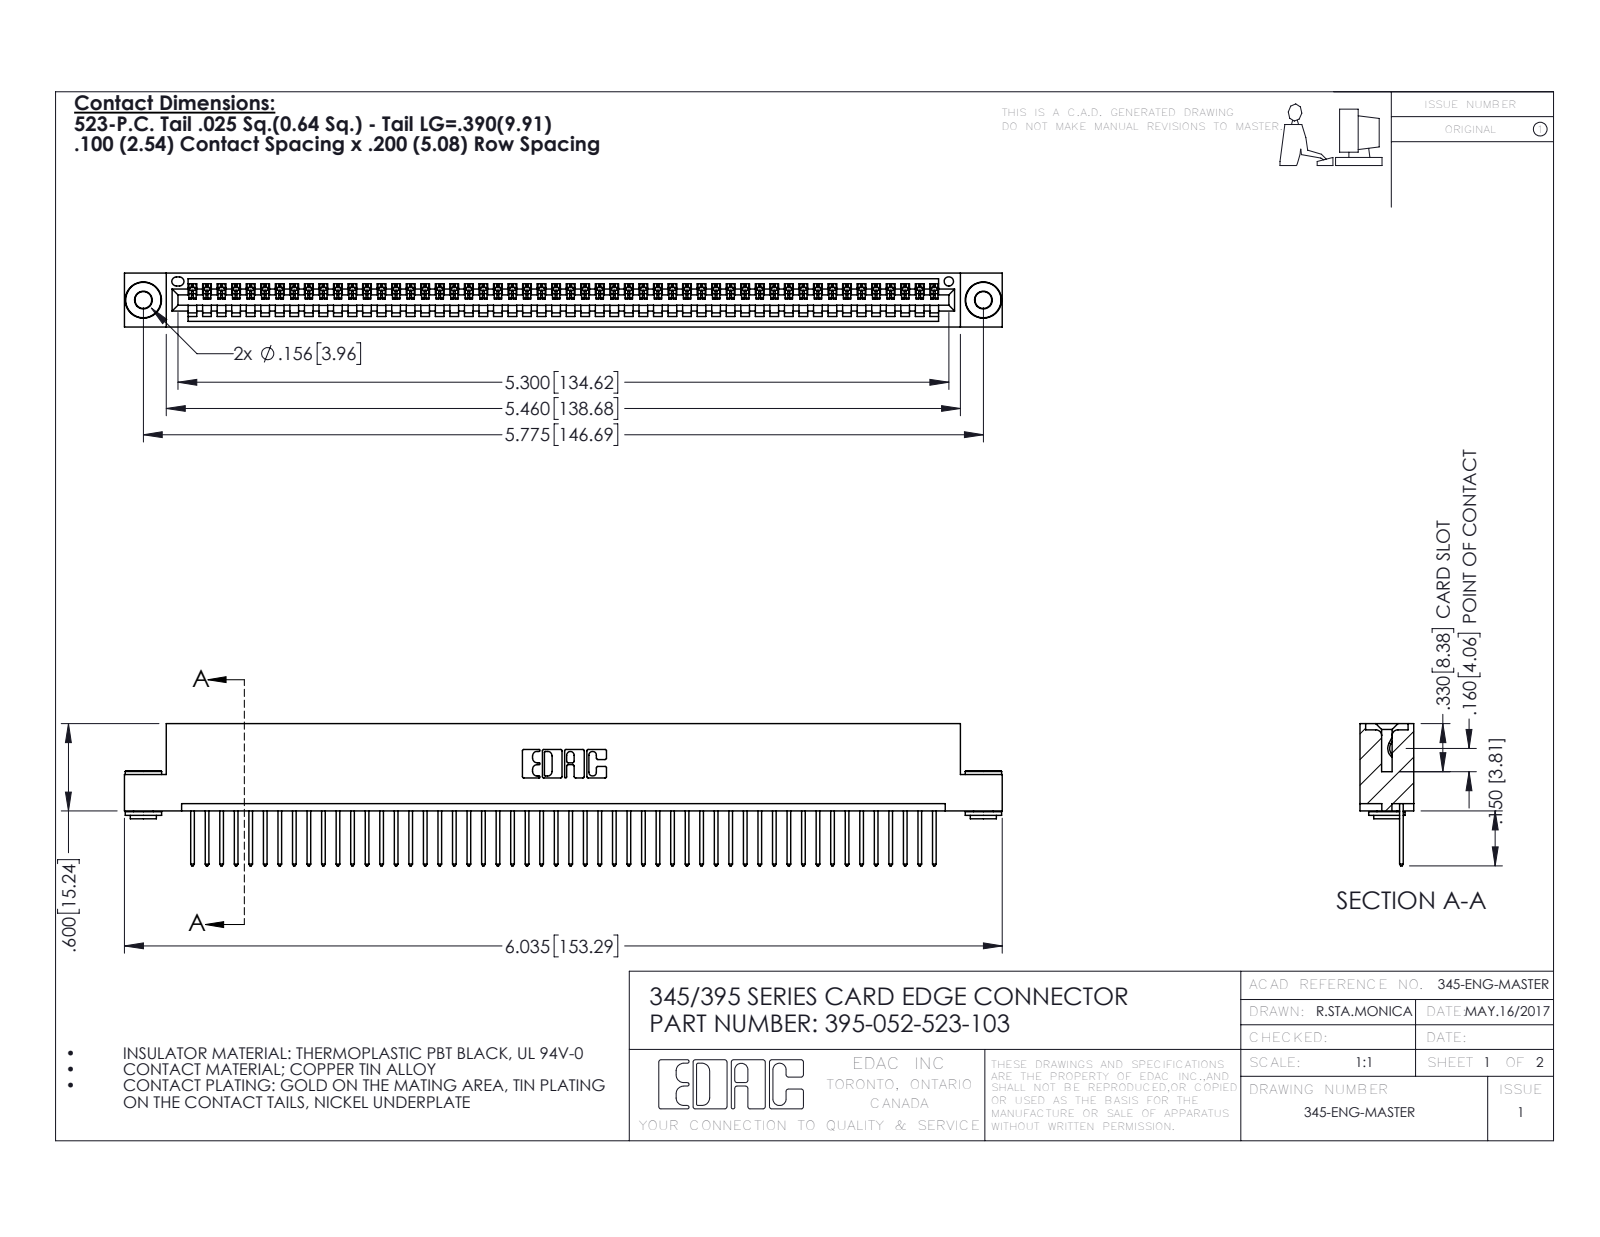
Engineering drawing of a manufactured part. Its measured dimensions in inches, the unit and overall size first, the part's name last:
Units: inches
Overall size (bounding box): 6.035 × 0.977 × 0.37
Round holes (diameter × count): ⌀0.116 ×2, ⌀0.156 ×2, ⌀0.064 ×1
Round bosses / shafts (diameter × count): ⌀0.25 ×2, ⌀0.18 ×2, ⌀0.136 ×2
Partial cylindrical surfaces — rounded edges, fillets, slot ends (radius × count): R0.006 ×104, R0.01 ×104, R0.01 ×22, R0.007 ×6, R0.031 ×6, R0.026 ×3, R0.031 ×2, R0.04 ×2
Main face-to-face distances: 0.072, 0.298, 0.37, 0.2, 0.025, 0.098, 0.272, 0.225, 0.149, 0.072
Hole centre spacings: 0.27, 5.539, 5.775
Volume: 0.893 in³ · Surface area: 30.79 in²
Bodies: 55 solids, 3180 faces (2170 planar, 1002 cylindrical, 8 other)
Part name (STEP PRODUCT): 345 Part_Flush Mounting Lugs - 0.156 Dia-TH; 345-250-002_345-250-002-102; 345-292-001_345-293-123; 395-052-523-103
STEP written by: SolidWorks 2016 (CONFIG_CONTROL_DESIGN)
